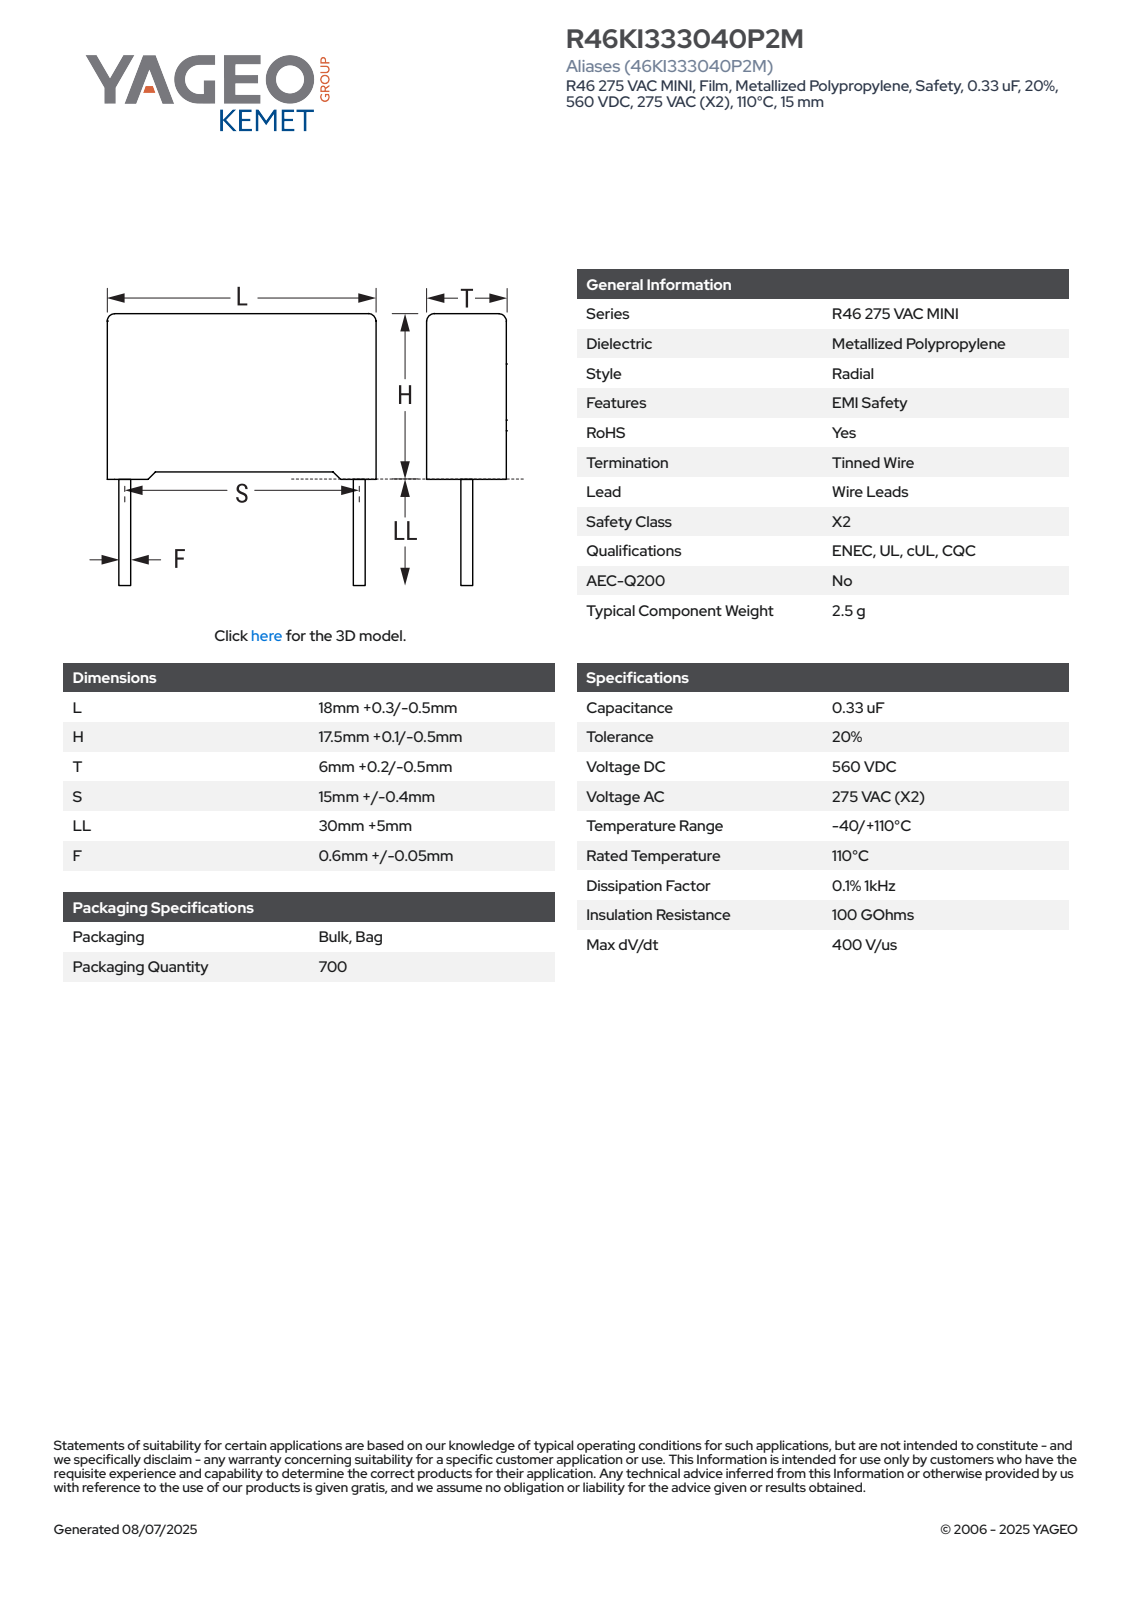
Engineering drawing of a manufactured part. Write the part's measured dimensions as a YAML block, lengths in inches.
part_name: "CFR_RB2_18X17.5X6_L18.3H17.6T6.2S15LL35F0.65"
step_written_by: "SolidWorks 2021 (AUTOMOTIVE_DESIGN)"
units: inches
bodies: {solids: 4, faces: 85, planar: 77, cylindrical: 8, other: 0}
overall_size: [2.071, 0.72, 0.244]
volume: 0.119
surface_area: 1.947
round_bosses_or_shafts:
  - {diameter: 0.026, count: 2}
partial_cylinders:
  - {radius: 0.02, count: 4}
face_to_face_distances: [0.244, 0.72, 0.663, 0.024, 0.03, 0.693, 0.669, 0.22, 0.696, 0.196]
